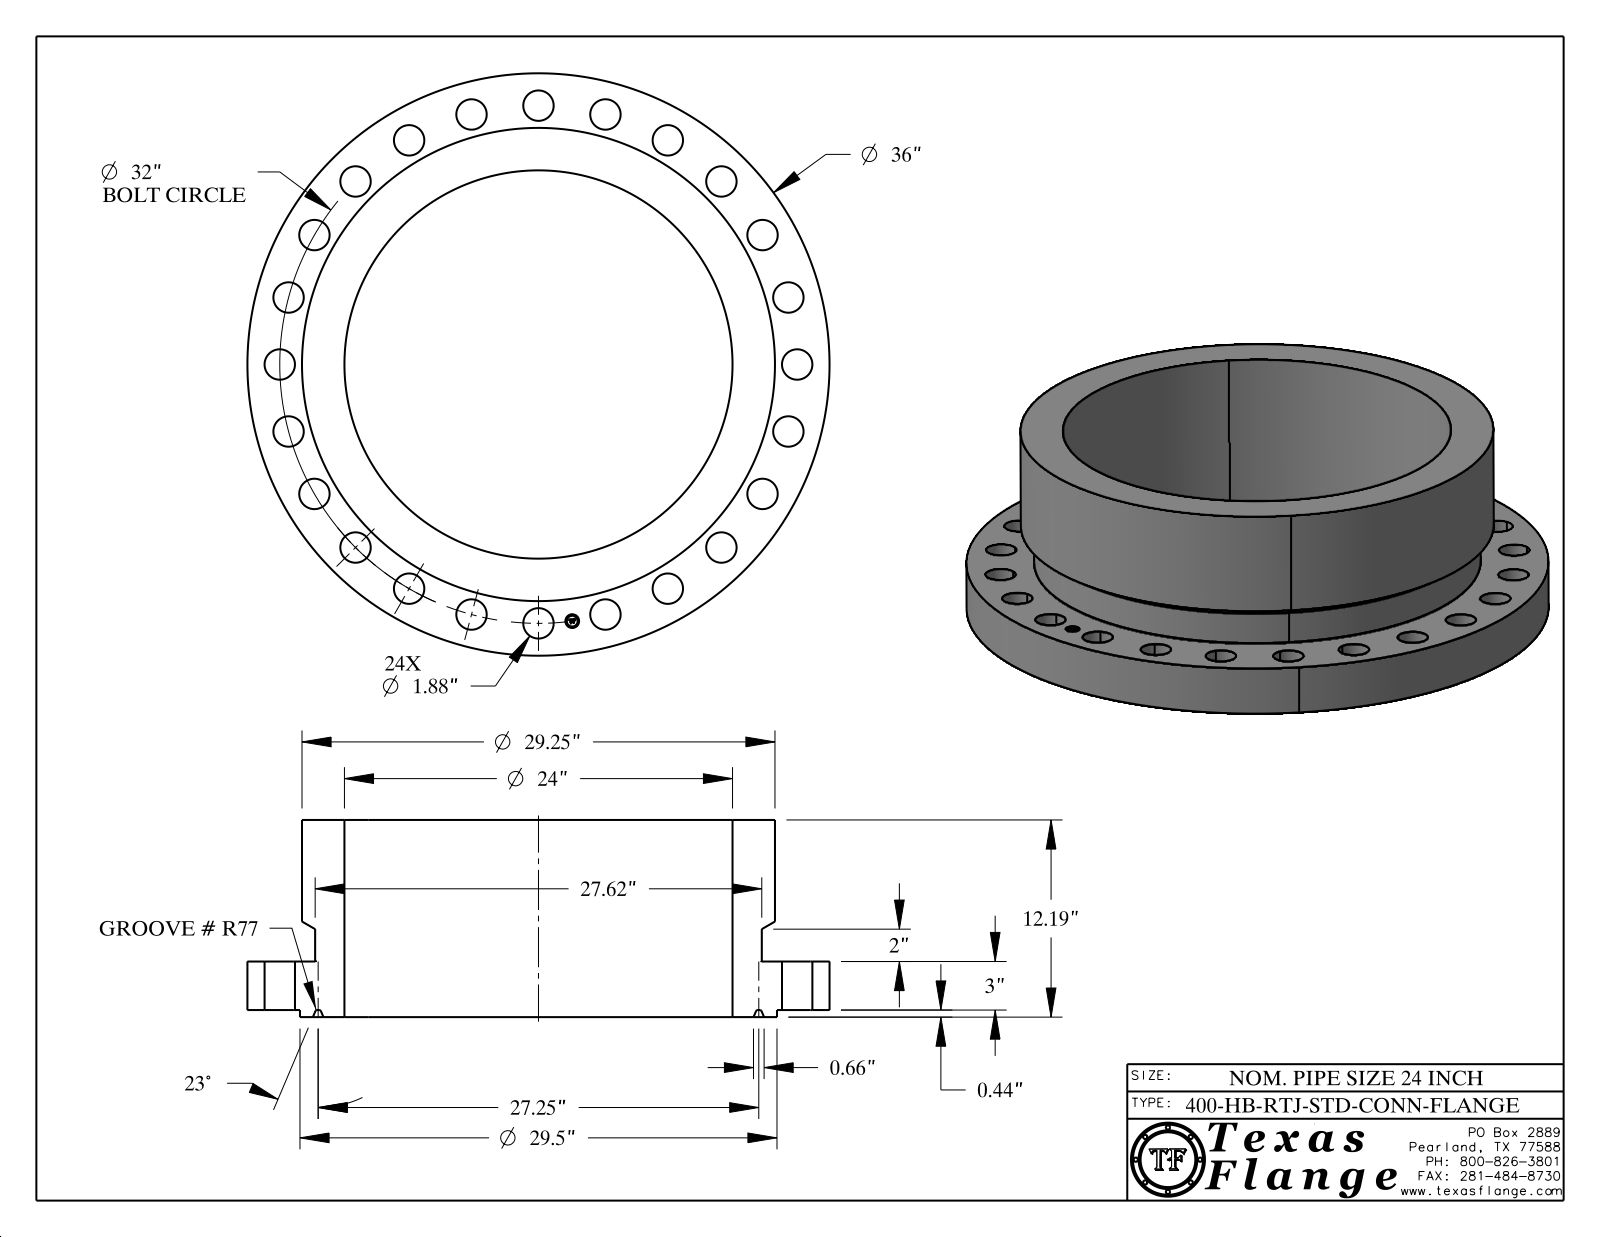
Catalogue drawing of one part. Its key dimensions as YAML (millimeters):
part_name: "24-400-HB-RTJ-STD-CONN-FLANGE"
step_written_by: "CATIA V5 STEP AP214 (AUTOMOTIVE_DESIGN)"
units: millimeters
bodies: {solids: 1, faces: 463, planar: 371, cylindrical: 78, other: 14}
overall_size: [914.4, 914.4, 309.6]
volume: 54700000
surface_area: 2375000
round_holes:
  - {diameter: 47.8, count: 24}
  - {diameter: 21.6, count: 1}
  - {diameter: 609.6, count: 1}
round_bosses_or_shafts:
  - {diameter: 1.3, count: 8}
  - {diameter: 914.4, count: 1}
  - {diameter: 749.3, count: 1}
  - {diameter: 743, count: 1}
  - {diameter: 701.5, count: 1}
  - {diameter: 17, count: 1}
face_to_face_distances: [76.2, 298.5, 222.3, 11.1, 87.3, 309.6, 87.2, 76.1, 222.4, 6.4]
hole_center_spacings: [406.4, 785.1, 106.1, 210.4, 311, 494.8, 574.7, 644.8]
